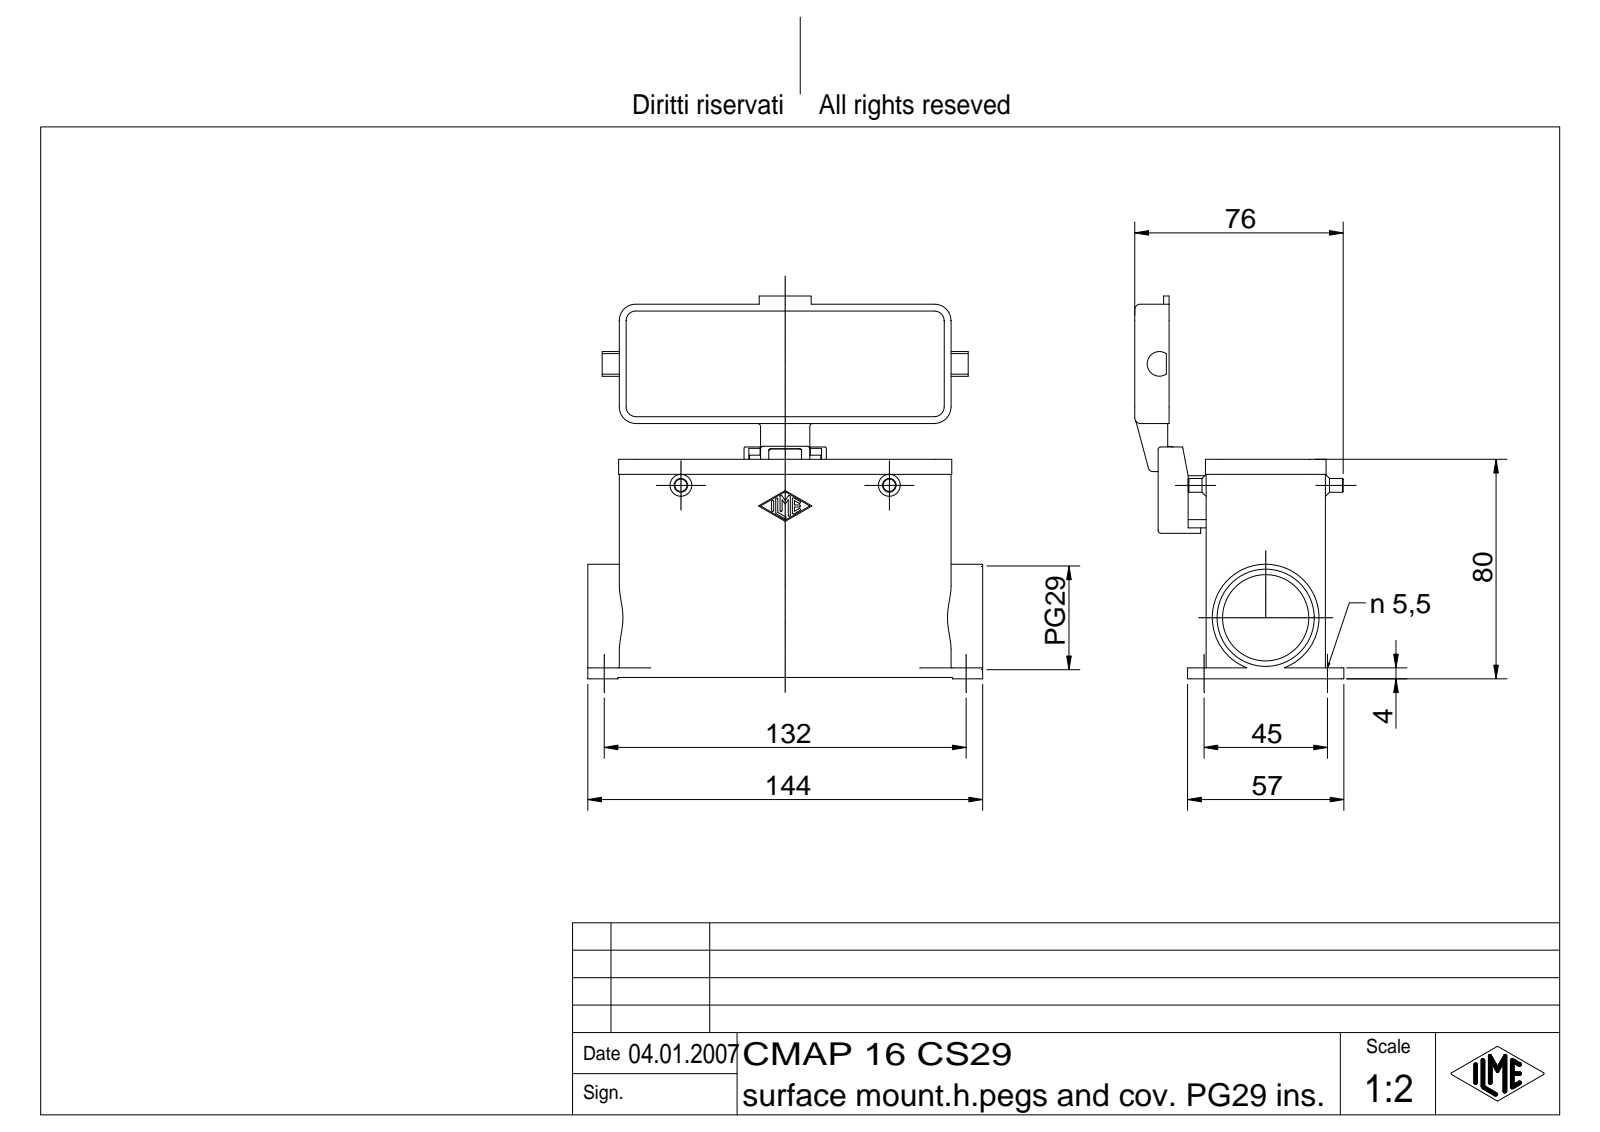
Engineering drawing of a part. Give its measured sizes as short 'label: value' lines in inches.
name: CMAP 16 CS29
written by: Autodesk Inventor 7 (AUTOMOTIVE_DESIGN)
unit: in
bodies: 2 solids, 479 faces (179 planar, 179 cylindrical, 121 other)
size: 5.669 × 5.492 × 3.002
volume: 9.472 in³; area: 140.1 in²
holes: 4× ⌀0.217, 1× ⌀0.157, 1× ⌀0.197, 1× ⌀1.239, 1× ⌀1.397
bosses: 2× ⌀0.197, 2× ⌀0.118, 1× ⌀1.535, 1× ⌀0.276, 1× ⌀0.157
rounds: 26× R0.039, 14× R0.015, 12× R0.236, 9× R0.02, 8× R0.028, 8× R0.079, 4× R0.118, 4× R0.138
face distances: 0.118, 1.594, 0.138, 1.713, 1.476, 2.736, 2.618, 0.886, 1.142, 1.024
hole spacings: 1.772, 5.197, 5.491
